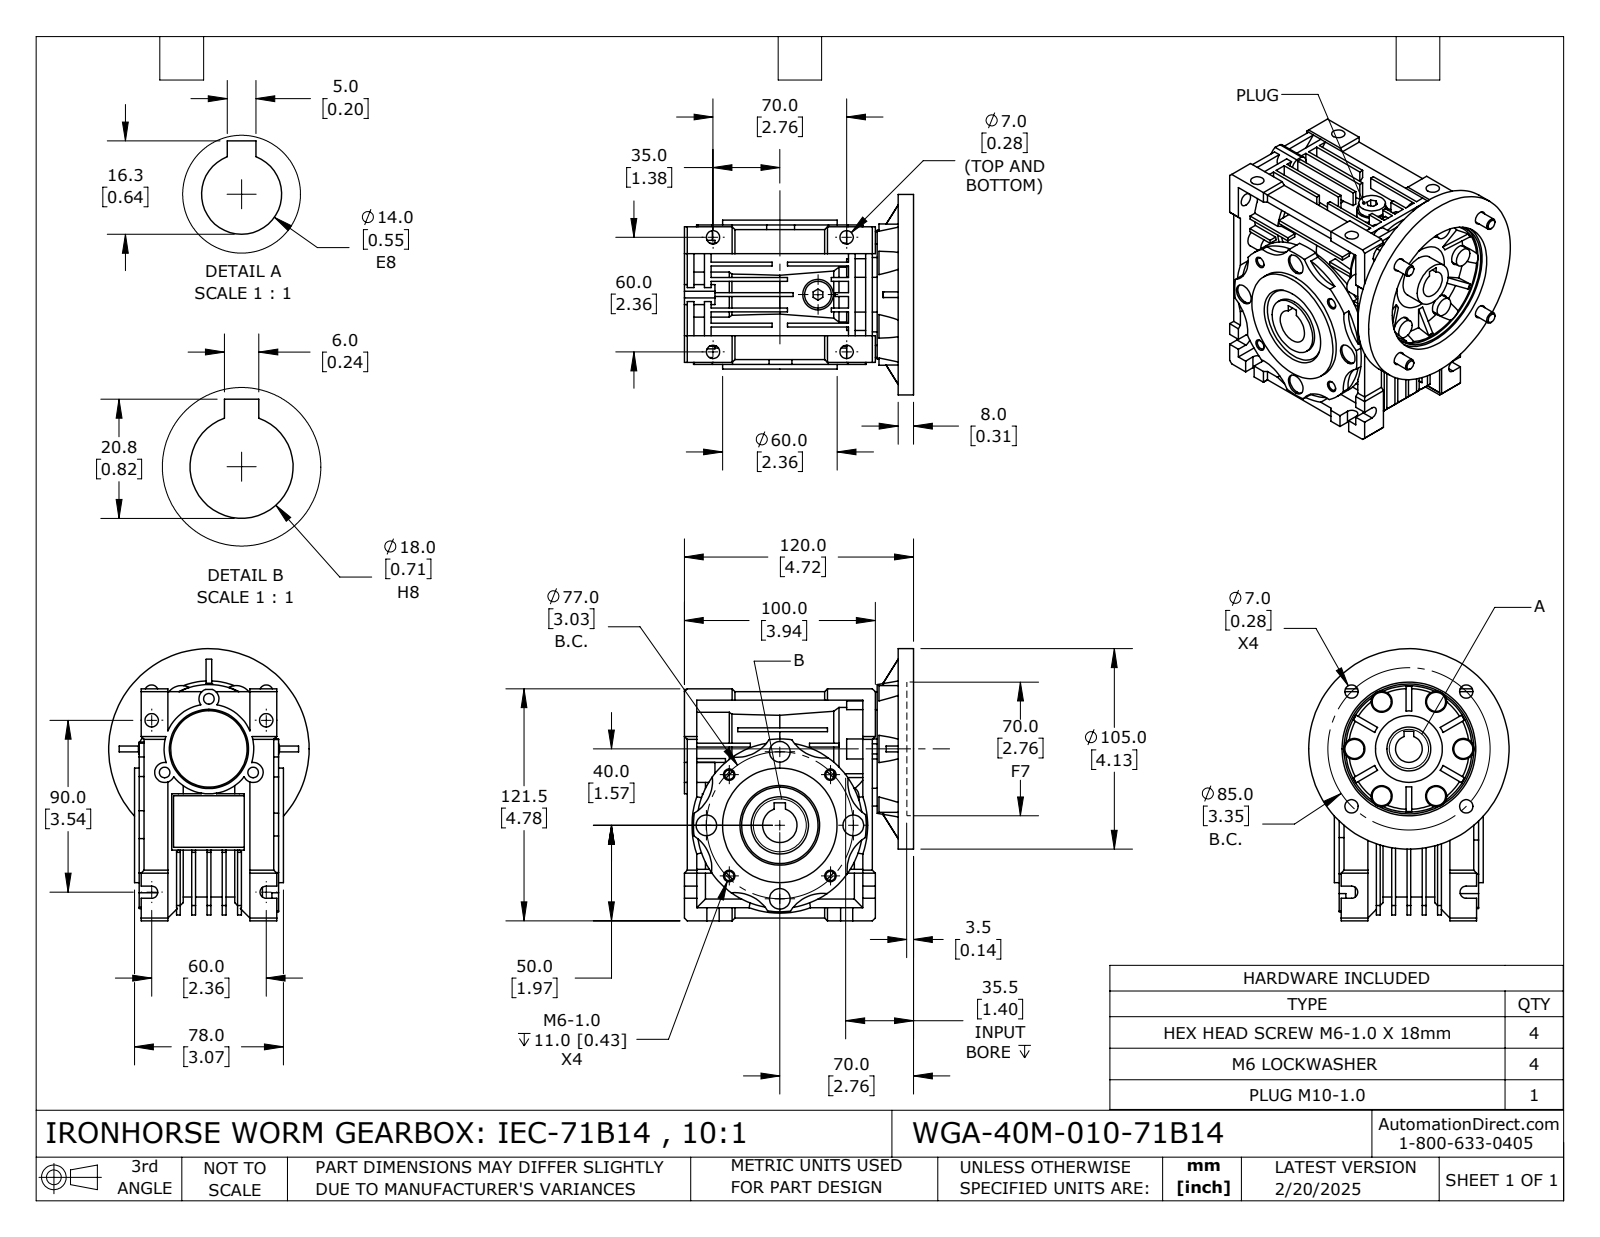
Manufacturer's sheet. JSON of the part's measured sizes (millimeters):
{"part_name": "WGA-40M-010-71B14", "step_written_by": "SolidWorks 2024 (CONFIG_CONTROL_DESIGN)", "units": "millimeters", "bodies": {"solids": 14, "faces": 956, "planar": 550, "cylindrical": 281, "other": 125}, "overall_size": [142.5, 128.5, 105], "volume_mm3": 688964, "surface_area_mm2": 170588, "round_holes": [[7, 10], [11, 6], [4.92, 4], [6.1, 4], [10.8, 4], [5.55, 3], [9, 1], [14, 1], [15, 1], [18, 1], [23, 1], [28, 1]], "round_bosses_or_shafts": [[10, 6], [12.2, 4], [6, 4], [105, 1], [75, 1], [60, 1], [54, 1], [47, 1]], "partial_cylinders_radius": [[20, 8], [3.2, 6], [5.22, 6], [8.5, 6], [5.25, 3], [34.31, 1], [43.5, 1], [43.59, 1]], "face_to_face_distances": [8, 6, 2, 1.5, 16, 10, 5, 11, 2.5, 24], "hole_center_spacings": [28.5, 29.1, 70.22, 49.36, 16.69, 30.09, 33.54, 37.5]}
